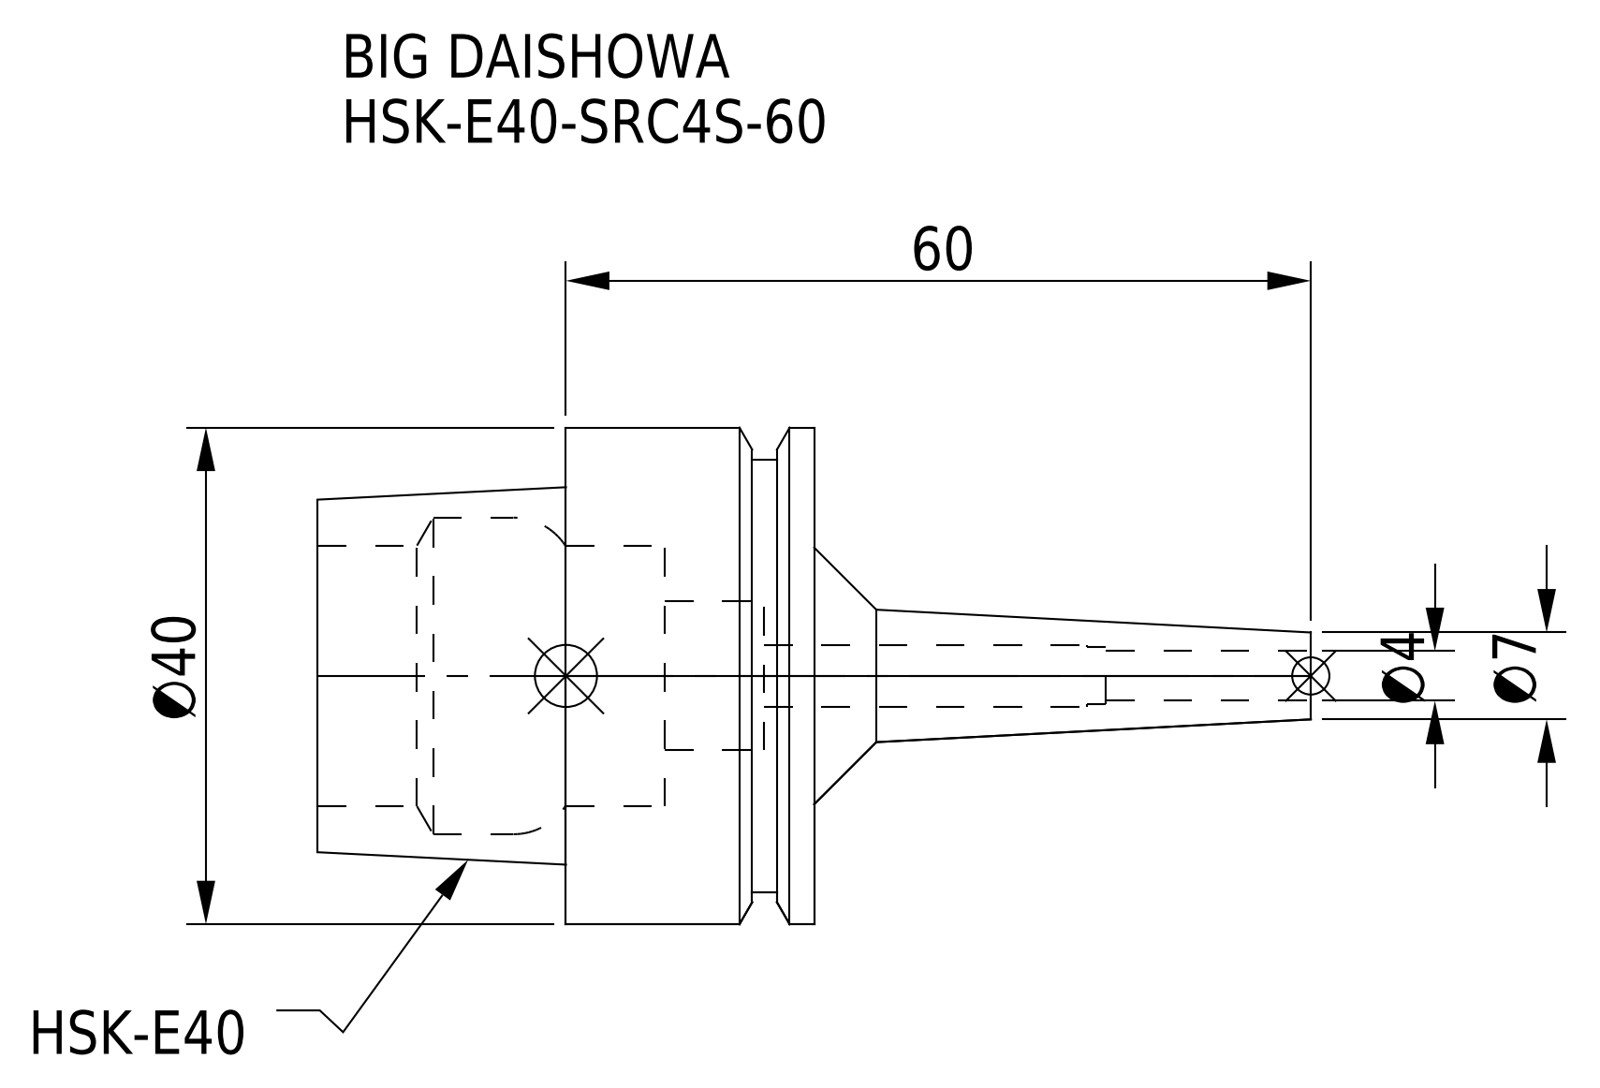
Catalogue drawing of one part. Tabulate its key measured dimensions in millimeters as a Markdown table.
| quantity | value |
| --- | --- |
| part name | HSK-E40-SRC4S-60 |
| STEP written by | CREO PARAMETRIC BY PTC INC, 2016380 (AUTOMOTIVE_DESIGN) |
| units | millimeters |
| bodies | 1 solid, 46 faces (10 planar, 22 cylindrical, 14 other) |
| overall size | 80 × 40 × 40 |
| volume | 28 086 mm³ |
| surface area | 11 246 mm² |
| round holes (diameter × count) | 4 × 1, 4.6 × 1, 5 × 1, 12 × 1, 21 × 1, 25.5 × 1 |
| round bosses / shafts (diameter × count) | 40 × 1, 34.8 × 1 |
| main face-to-face distances | 20, 40, 12.05, 7.95, 27.95, 4.05, 8, 15.95, 35.95, 5 |
